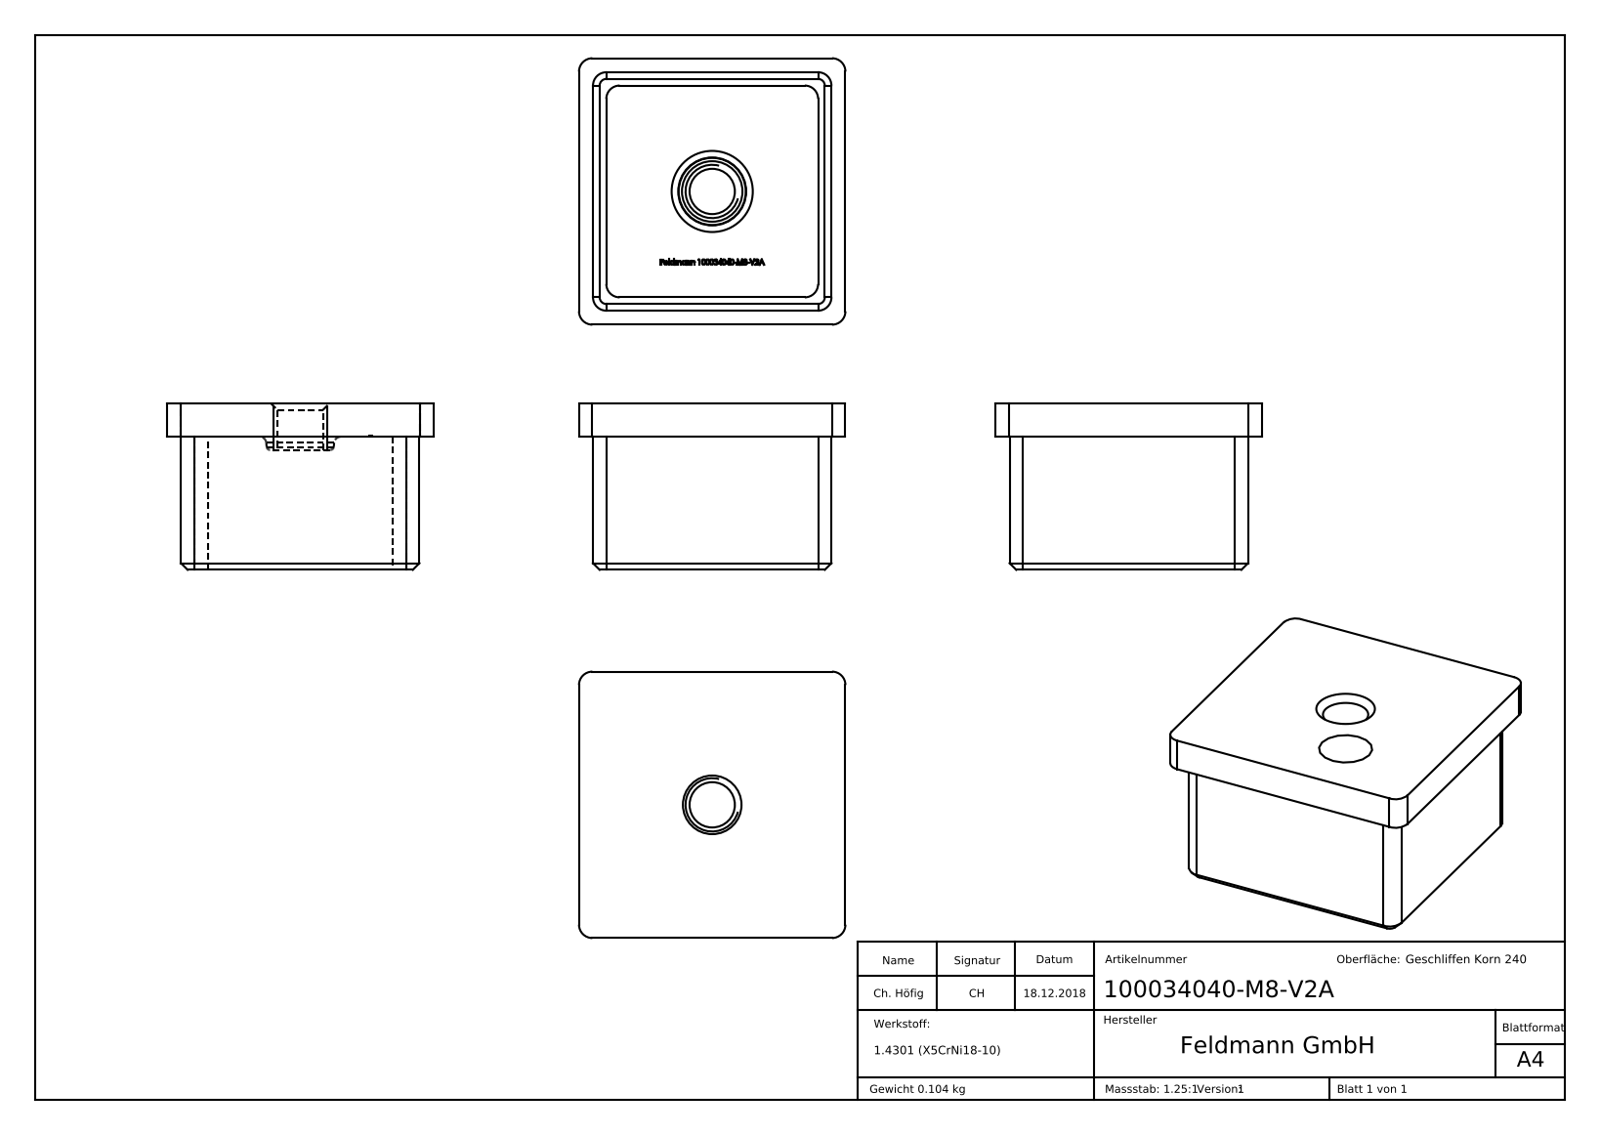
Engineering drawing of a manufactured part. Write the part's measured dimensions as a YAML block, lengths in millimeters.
part_name: "100034040-M8-V2A"
step_written_by: "SolidWorks 2015 (CONFIG_CONTROL_DESIGN)"
units: millimeters
bodies: {solids: 1, faces: 348, planar: 192, cylindrical: 14, other: 142}
overall_size: [40, 40, 25]
volume: 13223
surface_area: 9279
round_holes:
  - {diameter: 6.8, count: 1}
partial_cylinders:
  - {radius: 2, count: 12}
face_to_face_distances: [2, 33.8, 35.8, 5, 31.8, 2.1, 4.1, 35.9, 37.9, 40]
